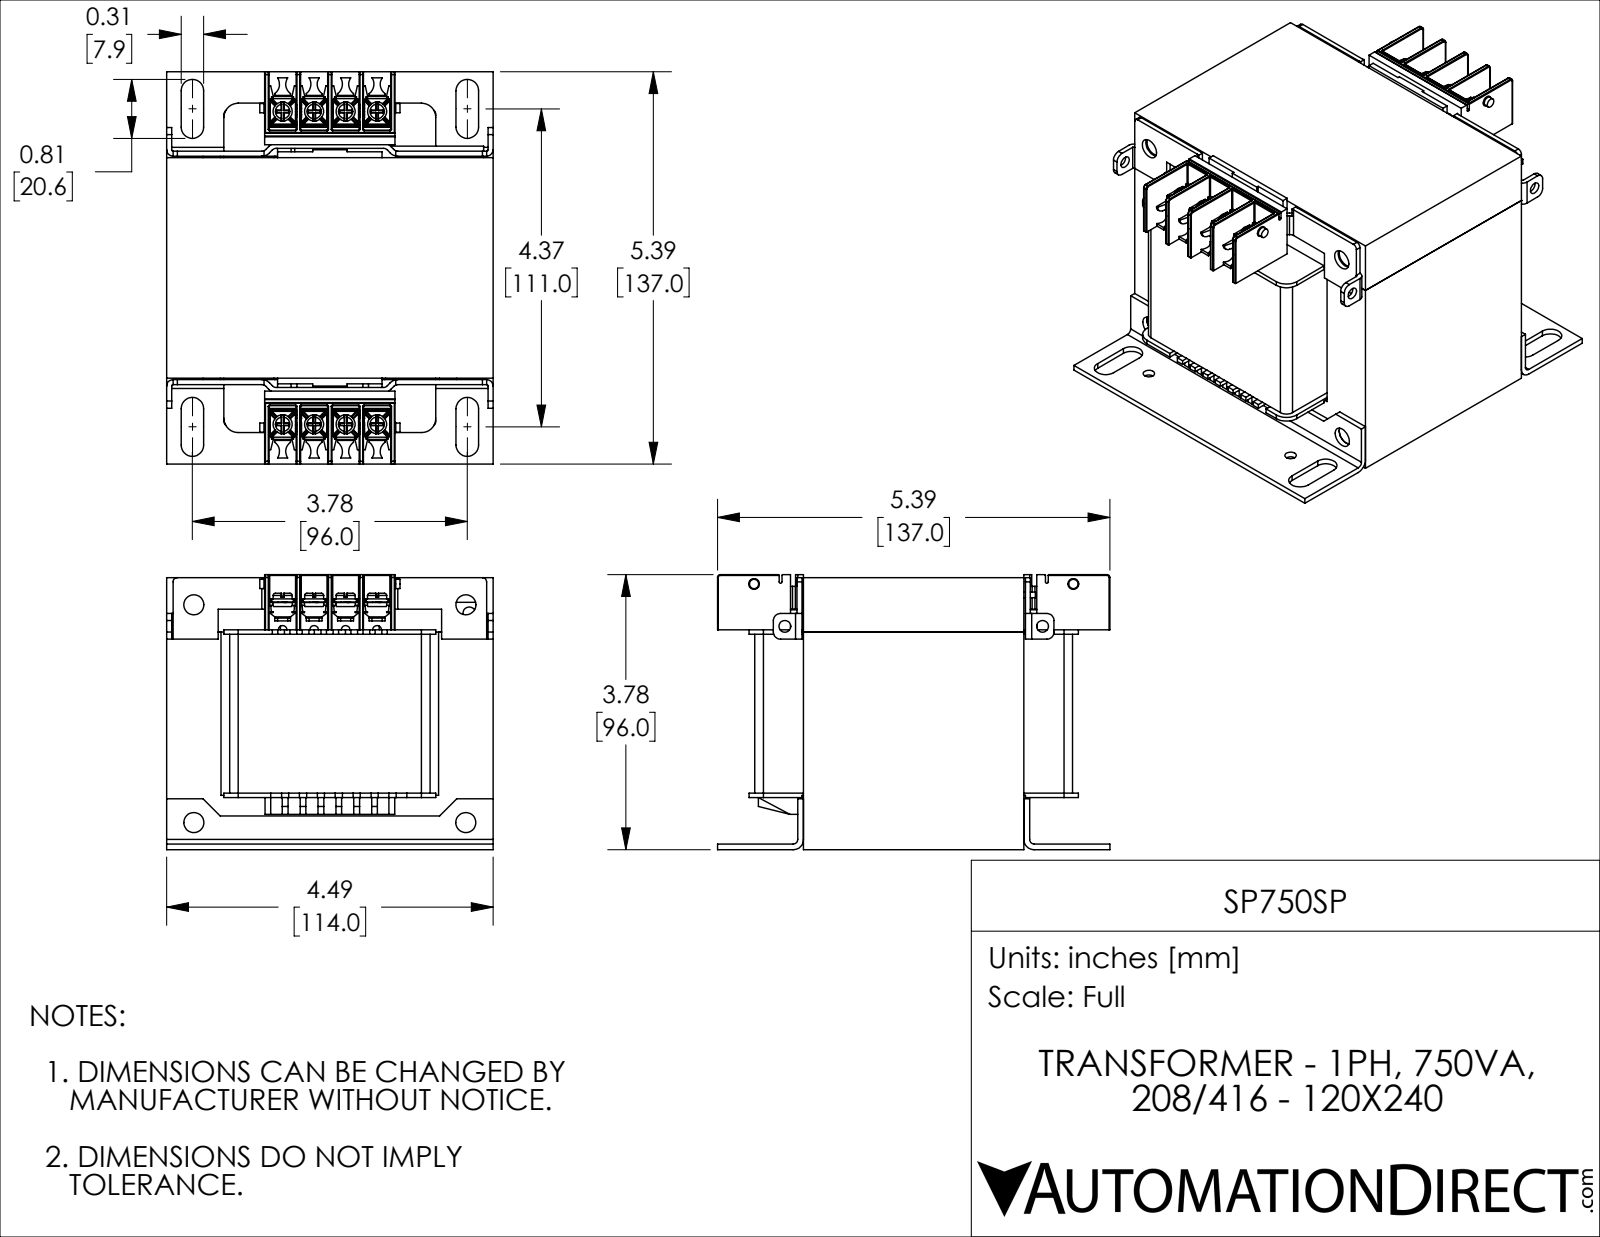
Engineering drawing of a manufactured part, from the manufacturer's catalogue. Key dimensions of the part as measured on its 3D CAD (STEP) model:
Part name (STEP PRODUCT): SP750SP
STEP written by: SolidWorks 2018 (AUTOMOTIVE_DESIGN)
Units: inches
Bodies: 42 solids, 3277 faces (2025 planar, 952 cylindrical, 300 other)
Overall size (bounding box): 5.394 × 4.488 × 3.781
Volume: 59.77 in³ · Surface area: 307.2 in²
Round holes (diameter × count): ⌀0.157 ×12, ⌀0.105 ×8, ⌀0.138 ×8, ⌀0.276 ×4, ⌀0.1 ×2, ⌀0.161 ×2, ⌀0.177 ×2
Round bosses / shafts (diameter × count): ⌀0.262 ×8, ⌀0.24 ×8, ⌀0.168 ×8, ⌀0.11 ×8, ⌀0.128 ×2
Partial cylindrical surfaces — rounded edges, fillets, slot ends (radius × count): R0.005 ×52, R0.01 ×52, R0.012 ×38, R0.029 ×32, R0.037 ×20, R0.157 ×16, R0.035 ×12, R0.079 ×10
Main face-to-face distances: 2.992, 0.748, 3.74, 0.866, 0.02, 1.496, 2.244, 3.622, 0.079, 3.031
Hole centre spacings: 0.433, 0.866, 4.311, 1.299, 1.595, 2.028, 4.289, 4.376
